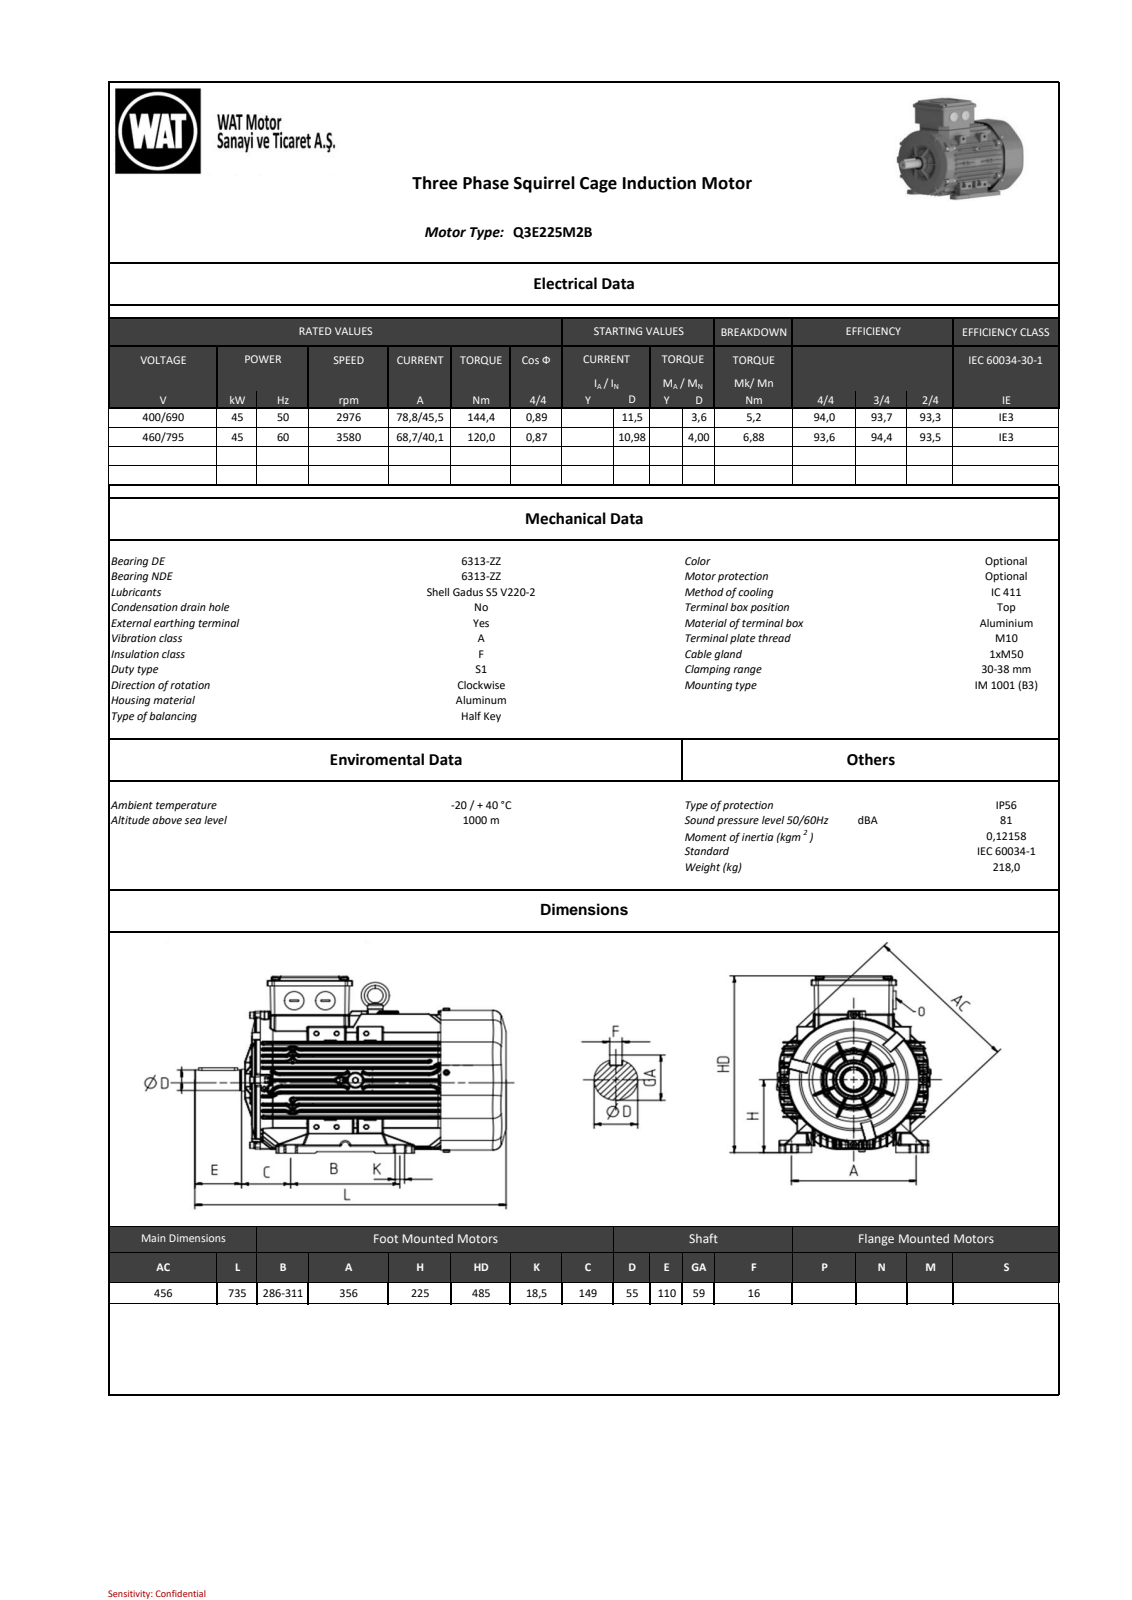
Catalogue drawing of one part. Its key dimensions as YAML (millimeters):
part_name: "AB_objects"
step_written_by: "SIEMENS PLM Software NX2206.8101 (AUTOMOTIVE_DESIGN)"
units: millimeters
bodies: {solids: 0, faces: 15092, planar: 6627, cylindrical: 2843, other: 5622}
overall_size: [736.99, 507.5, 442]
round_holes:
  - {diameter: 10.5, count: 8}
  - {diameter: 5, count: 7}
  - {diameter: 0.7, count: 6}
  - {diameter: 6, count: 5}
  - {diameter: 7.5, count: 5}
  - {diameter: 4.3, count: 4}
  - {diameter: 5.5, count: 4}
  - {diameter: 6.5, count: 4}
  - {diameter: 8.38, count: 4}
  - {diameter: 4, count: 3}
  - {diameter: 10.3, count: 3}
  - {diameter: 39.5, count: 2}
round_bosses_or_shafts:
  - {diameter: 10, count: 6}
  - {diameter: 16.5, count: 4}
  - {diameter: 16, count: 4}
  - {diameter: 5.85, count: 3}
  - {diameter: 58, count: 2}
  - {diameter: 55.1, count: 2}
  - {diameter: 52.3, count: 2}
  - {diameter: 52.2, count: 2}
partial_cylinders:
  - {radius: 1, count: 820}
  - {radius: 0.2, count: 332}
  - {radius: 2, count: 217}
  - {radius: 0.5, count: 166}
  - {radius: 3, count: 82}
  - {radius: 5, count: 81}
  - {radius: 2.5, count: 76}
  - {radius: 25, count: 44}
face_to_face_distances: [189.81, 15.53, 5, 169.04, 20.77, 14.83, 5.24, 184.57, 24.63, 150.23]
hole_center_spacings: [7.4, 156, 146.34, 68.18, 136, 12.82, 78.16, 156.54]
